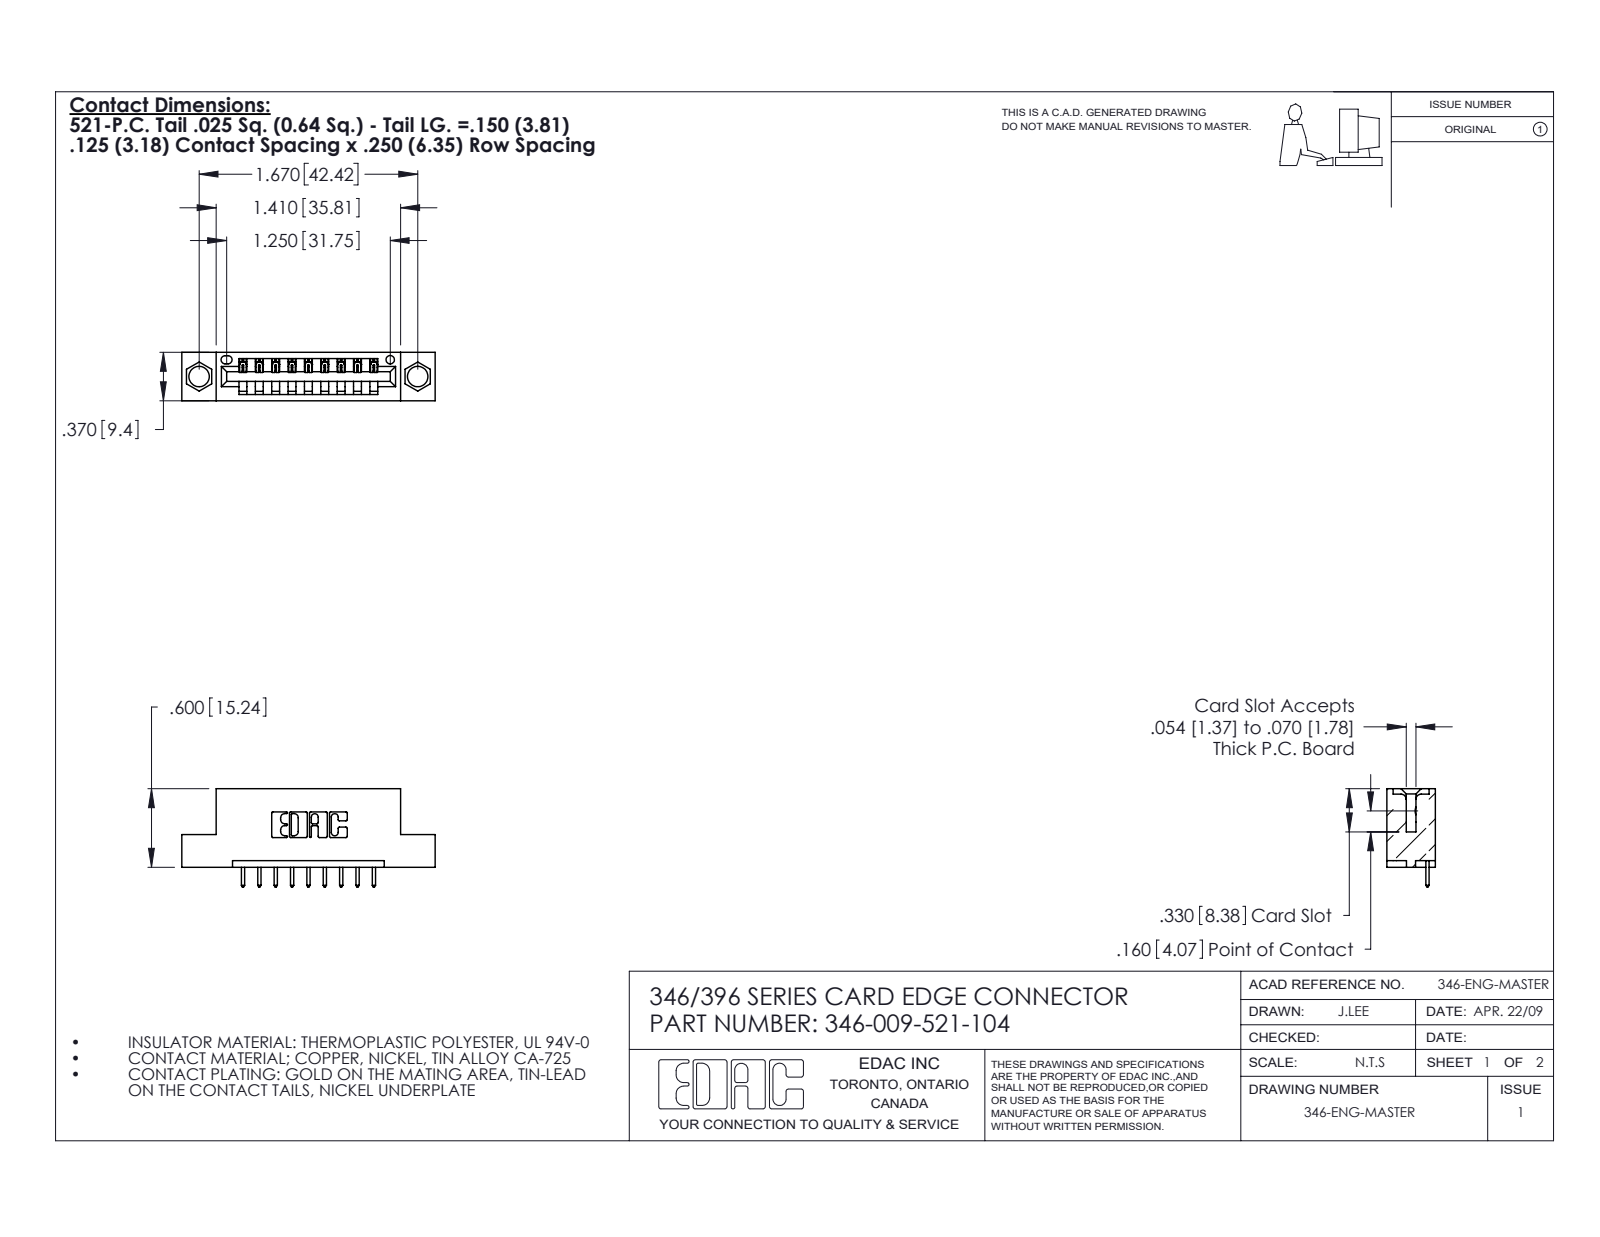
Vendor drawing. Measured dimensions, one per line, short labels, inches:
name: 345-292-001_345-293-121; 346 Part_Flush Mounting Lugs - 0.156 Dia-TH; 346-009-521-104
written by: SolidWorks 2020 (CONFIG_CONTROL_DESIGN)
unit: in
bodies: 10 solids, 658 faces (450 planar, 208 cylindrical, 0 other)
size: 1.935 × 0.75 × 0.37
volume: 0.265 in³; area: 7.457 in²
holes: 2× ⌀0.156, 1× ⌀0.064
rounds: 22× R0.01, 18× R0.006, 18× R0.01, 6× R0.007, 6× R0.031, 3× R0.026, 2× R0.031, 2× R0.04
face distances: 0.25, 0.37, 0.048, 0.322, 0.148, 0.222, 0.1, 0.174, 0.072, 0.298
hole spacings: 0.246, 1.465, 1.67
